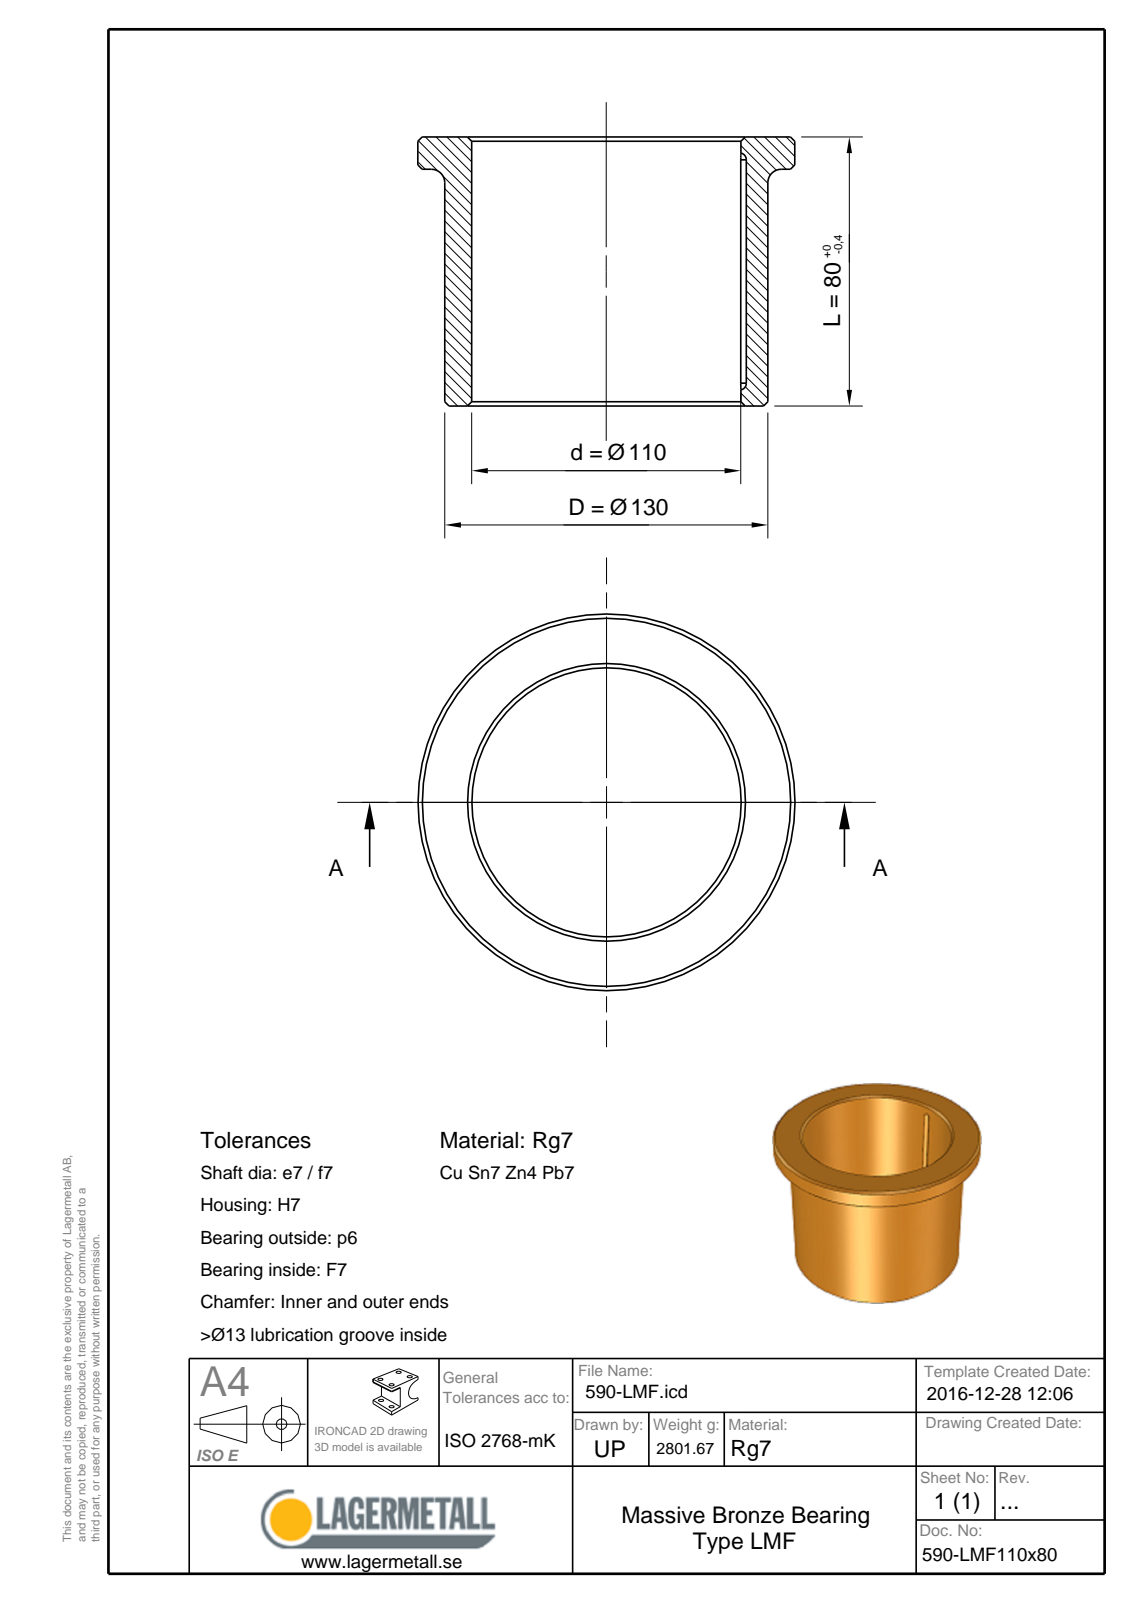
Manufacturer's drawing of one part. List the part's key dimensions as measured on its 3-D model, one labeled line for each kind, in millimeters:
Part name (STEP PRODUCT): 590-LMF110x80
STEP written by: Spatial InterOp 3D (CONFIG_CONTROL_DESIGN)
Units: millimetres
Bodies: 1 solid, 17 faces (4 planar, 5 cylindrical, 8 other)
Overall size (bounding box): 140 × 140 × 80
Volume: 318 372 mm³ · Surface area: 70 698 mm²
Round holes (diameter × count): ⌀110 ×1
Round bosses / shafts (diameter × count): ⌀140 ×1, ⌀130 ×1
Partial cylindrical surfaces — rounded edges, fillets, slot ends (radius × count): R1.75 ×2
Main face-to-face distances: 80, 72, 8
